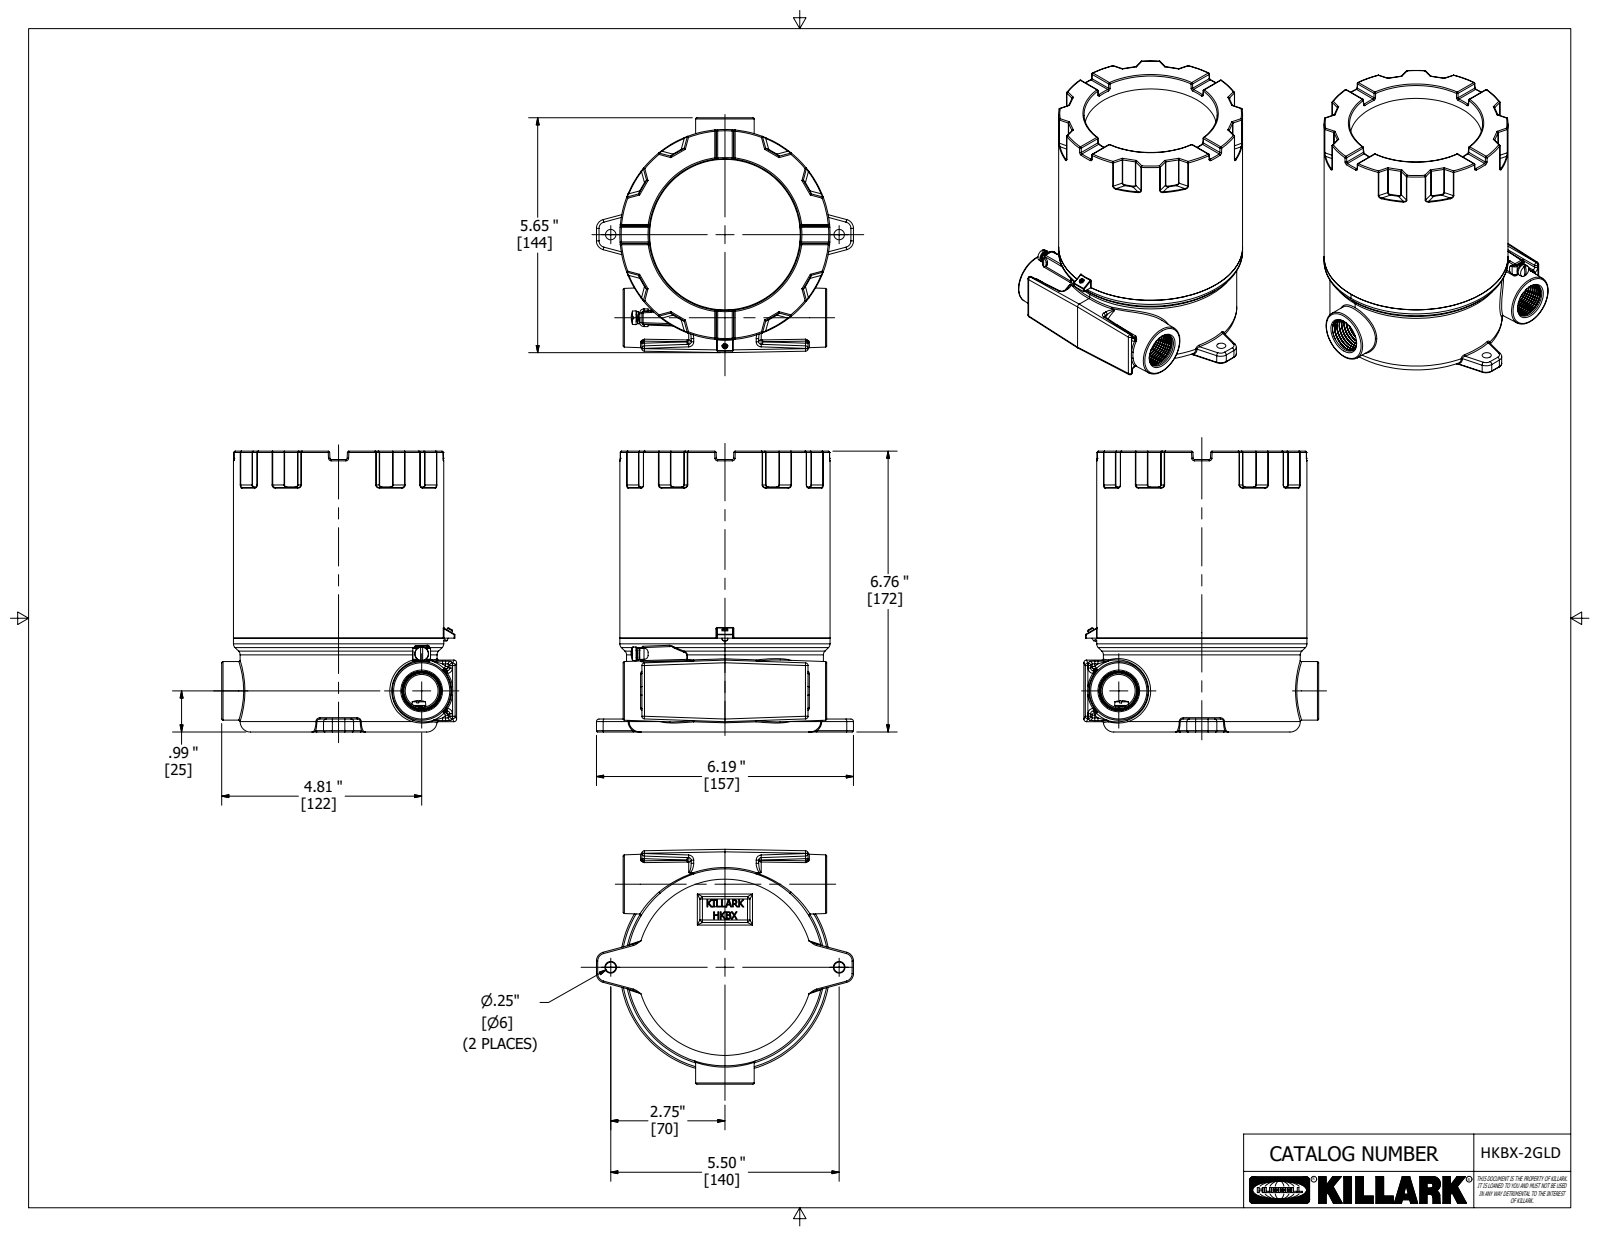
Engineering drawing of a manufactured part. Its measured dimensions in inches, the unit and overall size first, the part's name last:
Units: inches
Overall size (bounding box): 24.949 × 14.924 × 6.758
Round holes (diameter × count): ⌀0.125 ×4, ⌀0.13 ×2, ⌀0.18 ×2, ⌀0.25 ×2, ⌀0.104 ×1, ⌀0.792 ×1, ⌀3.625 ×1, ⌀3.625 ×1, ⌀3.881 ×1, ⌀4.1 ×1, ⌀4.34 ×1, ⌀4.39 ×1
Round bosses / shafts (diameter × count): ⌀0.293 ×2, ⌀0.158 ×2, ⌀5.06 ×1, ⌀4.74 ×1, ⌀4.724 ×1, ⌀4.585 ×1, ⌀4.331 ×1, ⌀4.204 ×1
Partial cylindrical surfaces — rounded edges, fillets, slot ends (radius × count): R0.062 ×51, R0.016 ×47, R0.031 ×45, R0.125 ×8, R0.05 ×4, R0.094 ×4, R0.1 ×4, R0.219 ×4
Main face-to-face distances: 5.931, 6.307, 0.375, 0.25, 5.681, 6.057, 0.013, 6.758, 6.508, 0.827
Hole centre spacings: 2.869, 2.029, 2.75, 3.361, 0.757, 0.892, 1.15, 1.15
Volume: 54.28 in³ · Surface area: 683.9 in²
Bodies: 16 solids, 1006 faces (332 planar, 242 cylindrical, 432 other)
Part name (STEP PRODUCT): KIL_HKBX-2GLD; 51641ABAM for web; 51640ABAM for web; 51643AAAB (+7 more)
STEP written by: Autodesk Inventor 2020 (AUTOMOTIVE_DESIGN)
